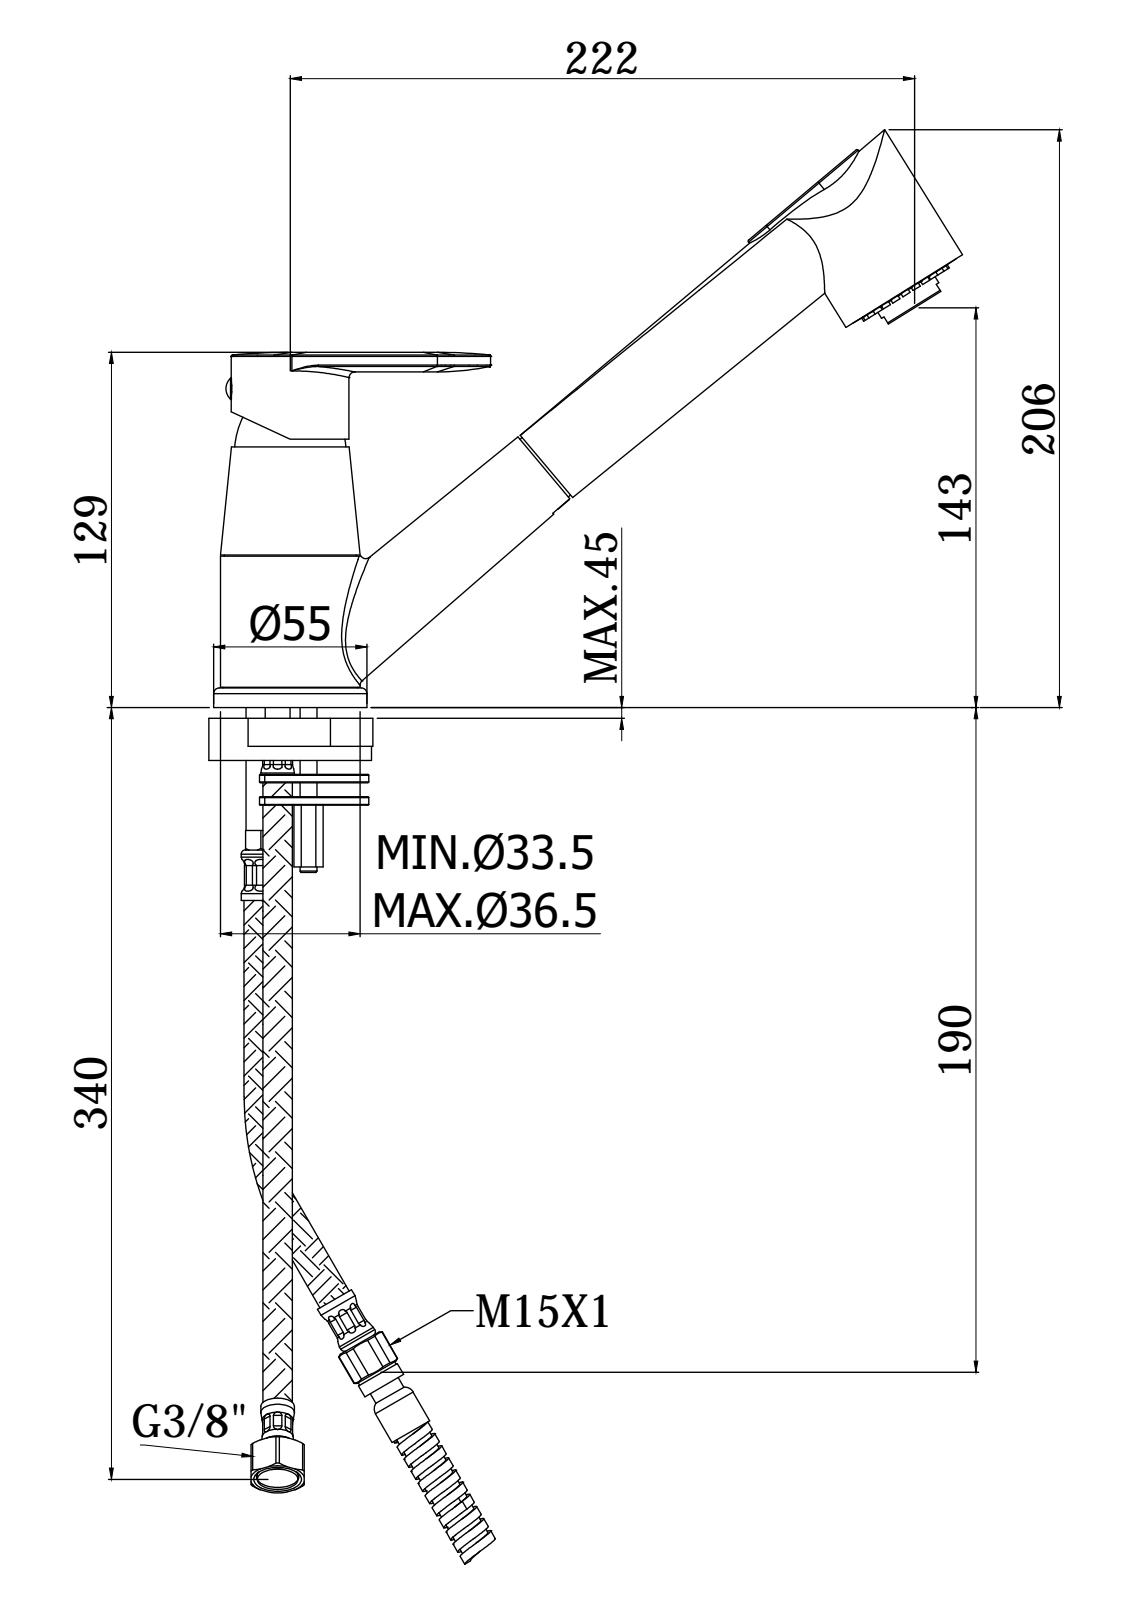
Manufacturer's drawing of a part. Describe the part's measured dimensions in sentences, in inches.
The part is named "CA183CR". Its 3-D file was written by "CREO PARAMETRIC BY PTC INC, 2020044 (CONFIG_CONTROL_DESIGN)". It is 5 solids with 331 faces: 102 planar, 114 cylindrical and 115 other. Overall it measures 9.737 by 7.438 by 2.154 inches. Its volume is 17.24 cubic inches and its surface area 148.7 square inches. Round holes: 1 of diameter 0.118, 1 of diameter 0.177, 1 of diameter 0.217, 1 of diameter 0.945, 1 of diameter 0.965, 1 of diameter 0.98, 1 of diameter 1.205, 1 of diameter 1.417, 1 of diameter 1.594, 1 of diameter 1.894. Round bosses or shafts: 24 of diameter 0.118, 1 of diameter 2.154, 1 of diameter 1.969, 1 of diameter 1.929, 1 of diameter 1.732, 1 of diameter 1.654, 1 of diameter 1.102, 1 of diameter 0.961. Partial cylindrical surfaces (rounded edges, fillets, slot ends): 4 of radius 0.118, 2 of radius 1.969, 1 of radius 0.098, 1 of radius 0.138, 1 of radius 0.315, 1 of radius 0.453, 1 of radius 0.512, 1 of radius 0.768. The main face-to-face distances are 0.276, 2.134, 1.858, 2.132, 1.857, 4.862, 4.587, 2.73, 2.728, 0.096.
